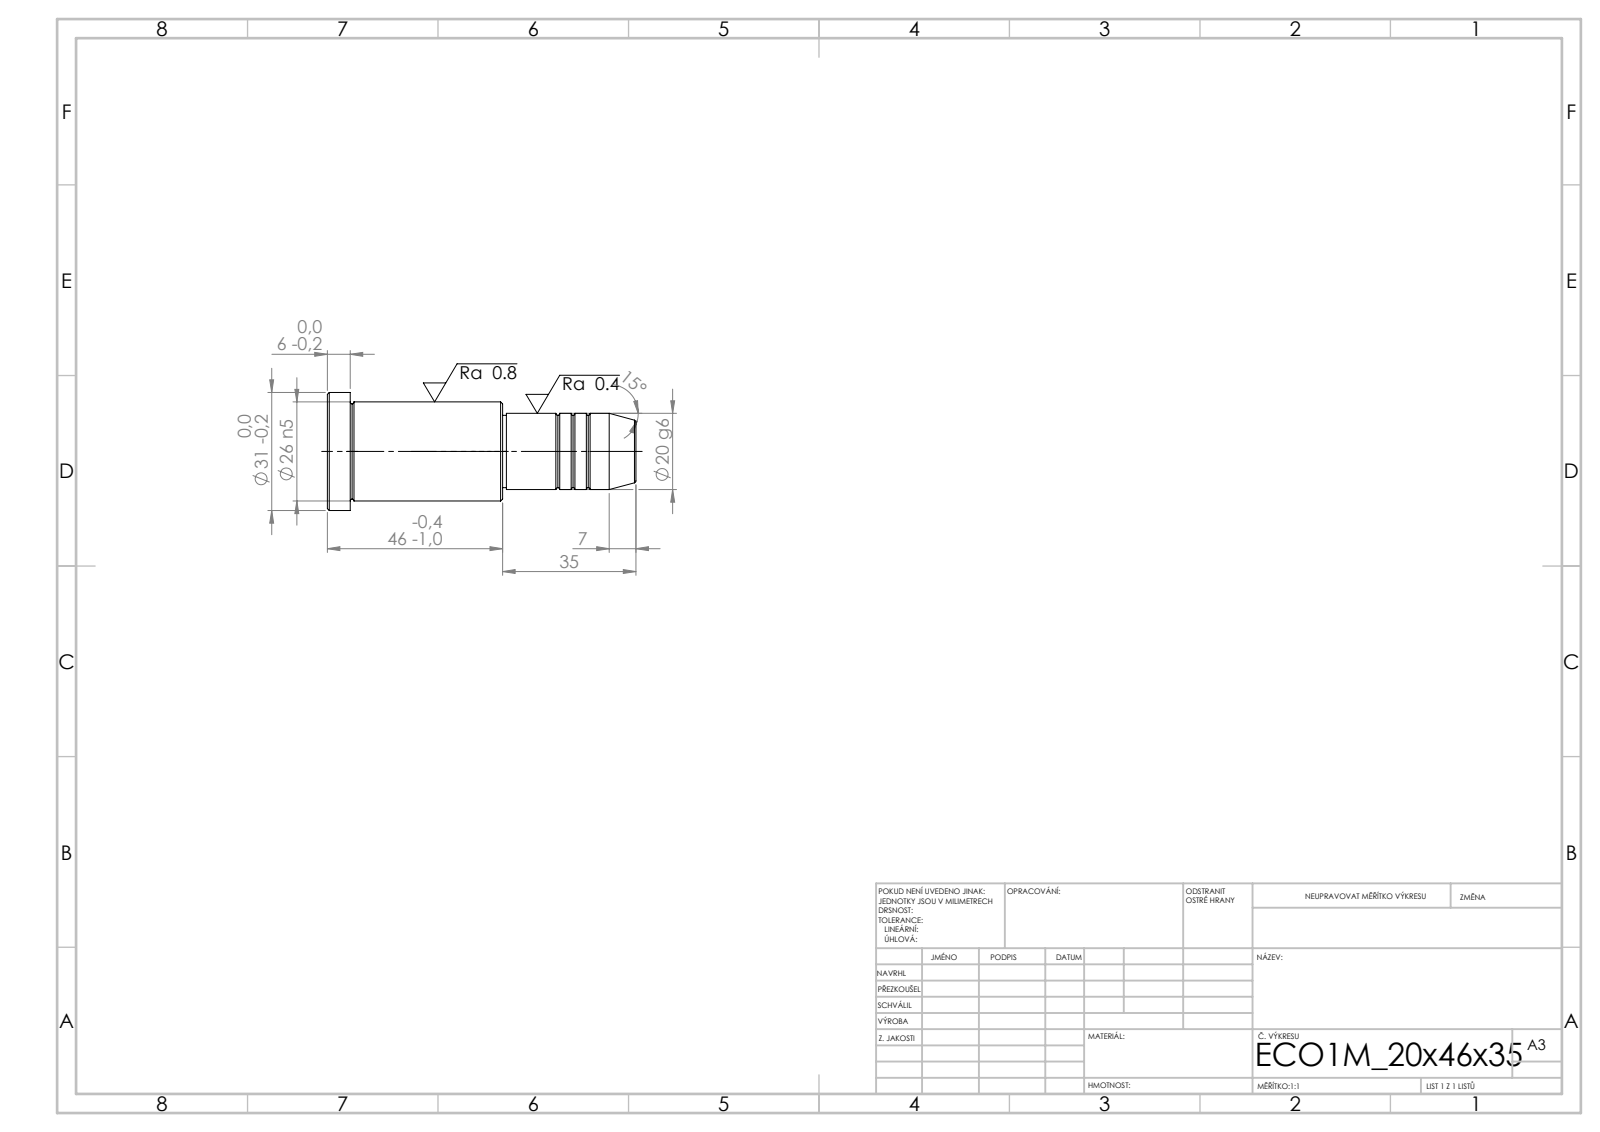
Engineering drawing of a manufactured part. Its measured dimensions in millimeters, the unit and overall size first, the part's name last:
Units: millimetres
Overall size (bounding box): 81 × 31 × 31
Round bosses / shafts (diameter × count): ⌀31 ×1, ⌀26 ×1, ⌀20 ×1, ⌀19 ×1
Main face-to-face distances: 6, 40, 46, 35, 75, 81, 34, 1, 41, 47
Volume: 36 216 mm³ · Surface area: 7 567 mm²
Bodies: 1 solid, 43 faces (5 planar, 14 cylindrical, 24 other)
STEP written by: SolidWorks 2019 (CONFIG_CONTROL_DESIGN)
